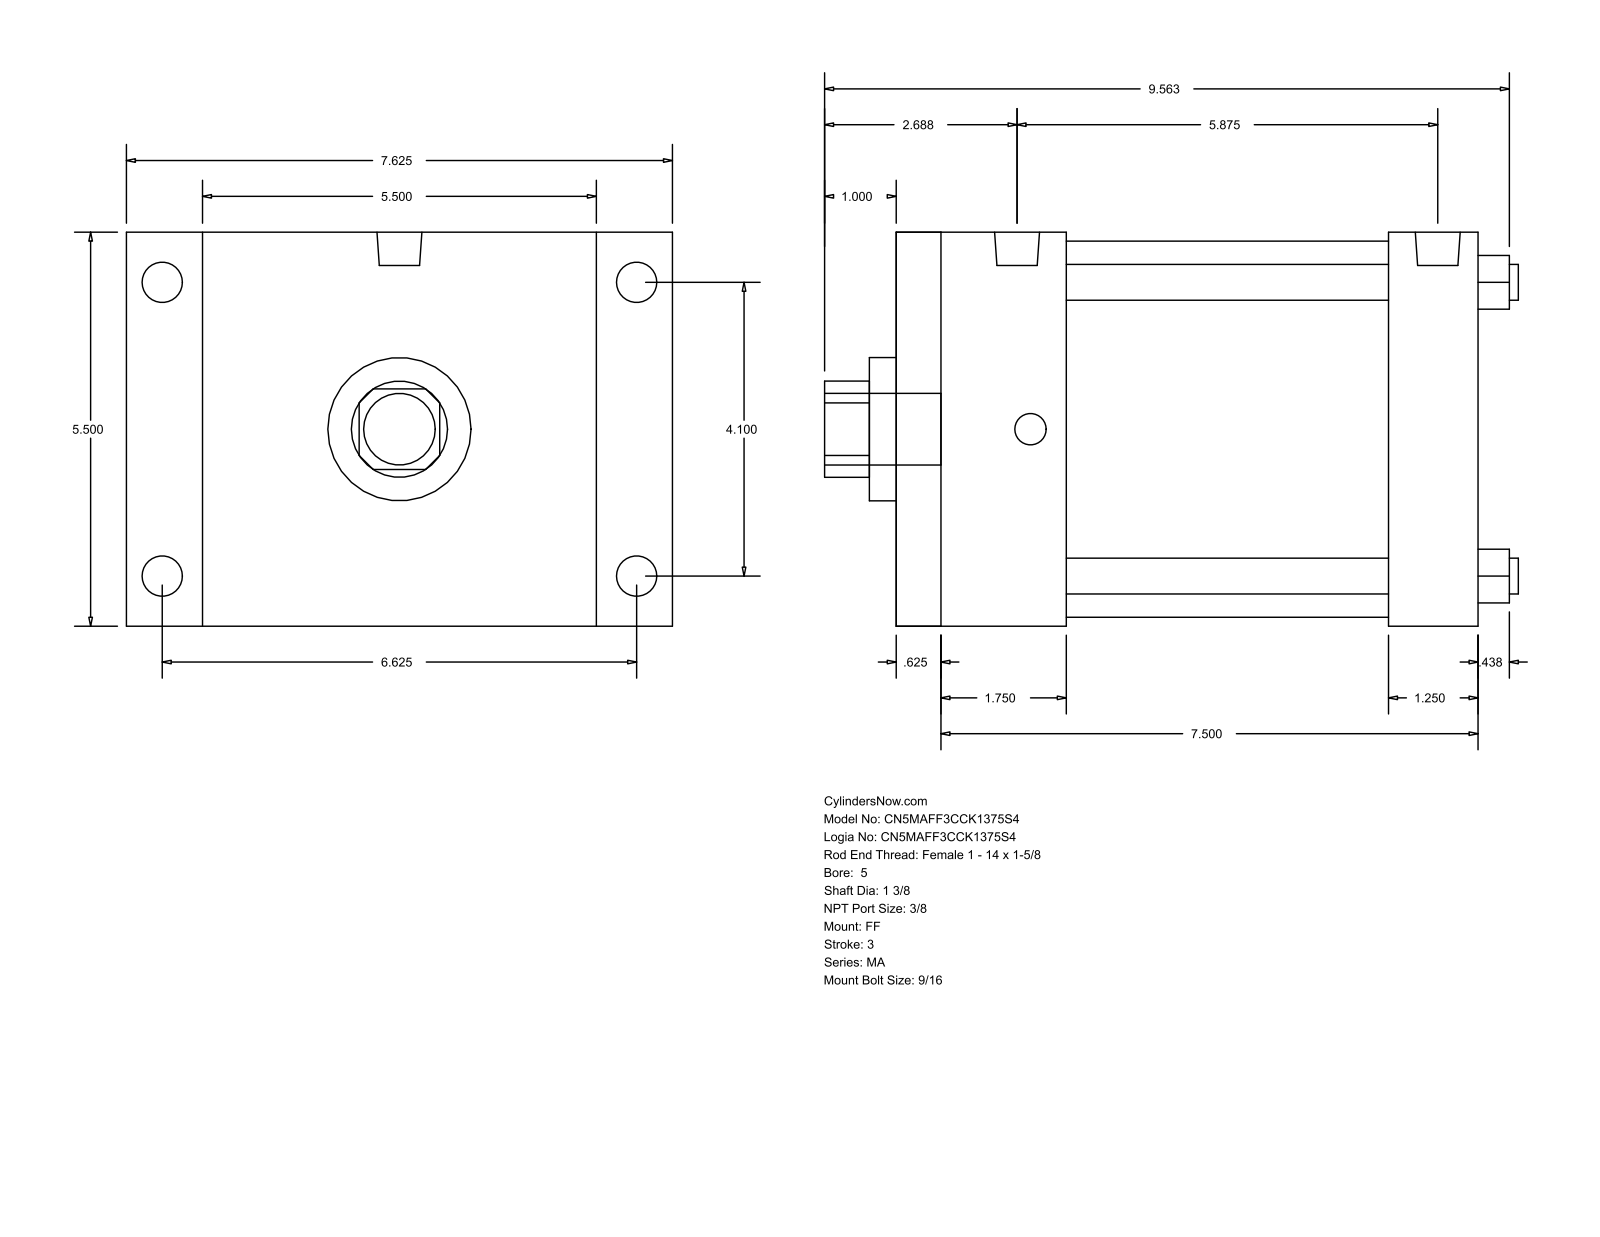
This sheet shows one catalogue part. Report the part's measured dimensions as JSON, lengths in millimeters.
{"part_name": "MA_FF__0500_1.375", "step_written_by": "GSSL Pune (CONFIG_CONTROL_DESIGN)", "units": "millimeters", "bodies": {"solids": 0, "faces": 92, "planar": 64, "cylindrical": 28, "other": 0}, "overall_size": [246.06, 193.68, 139.7], "round_holes": [[12.7, 4], [34.92, 1], [50.8, 1], [133.35, 1]], "round_bosses_or_shafts": [[14.29, 4], [11.11, 4], [15.93, 2], [25.4, 1]], "partial_cylinders_radius": [[17.06, 1]], "face_to_face_distances": [139.7, 206.38, 15.87, 190.51, 174.63, 158.76, 31.75, 60.32, 44.45, 114.31], "hole_center_spacings": [73.64, 104.14, 147.28]}
